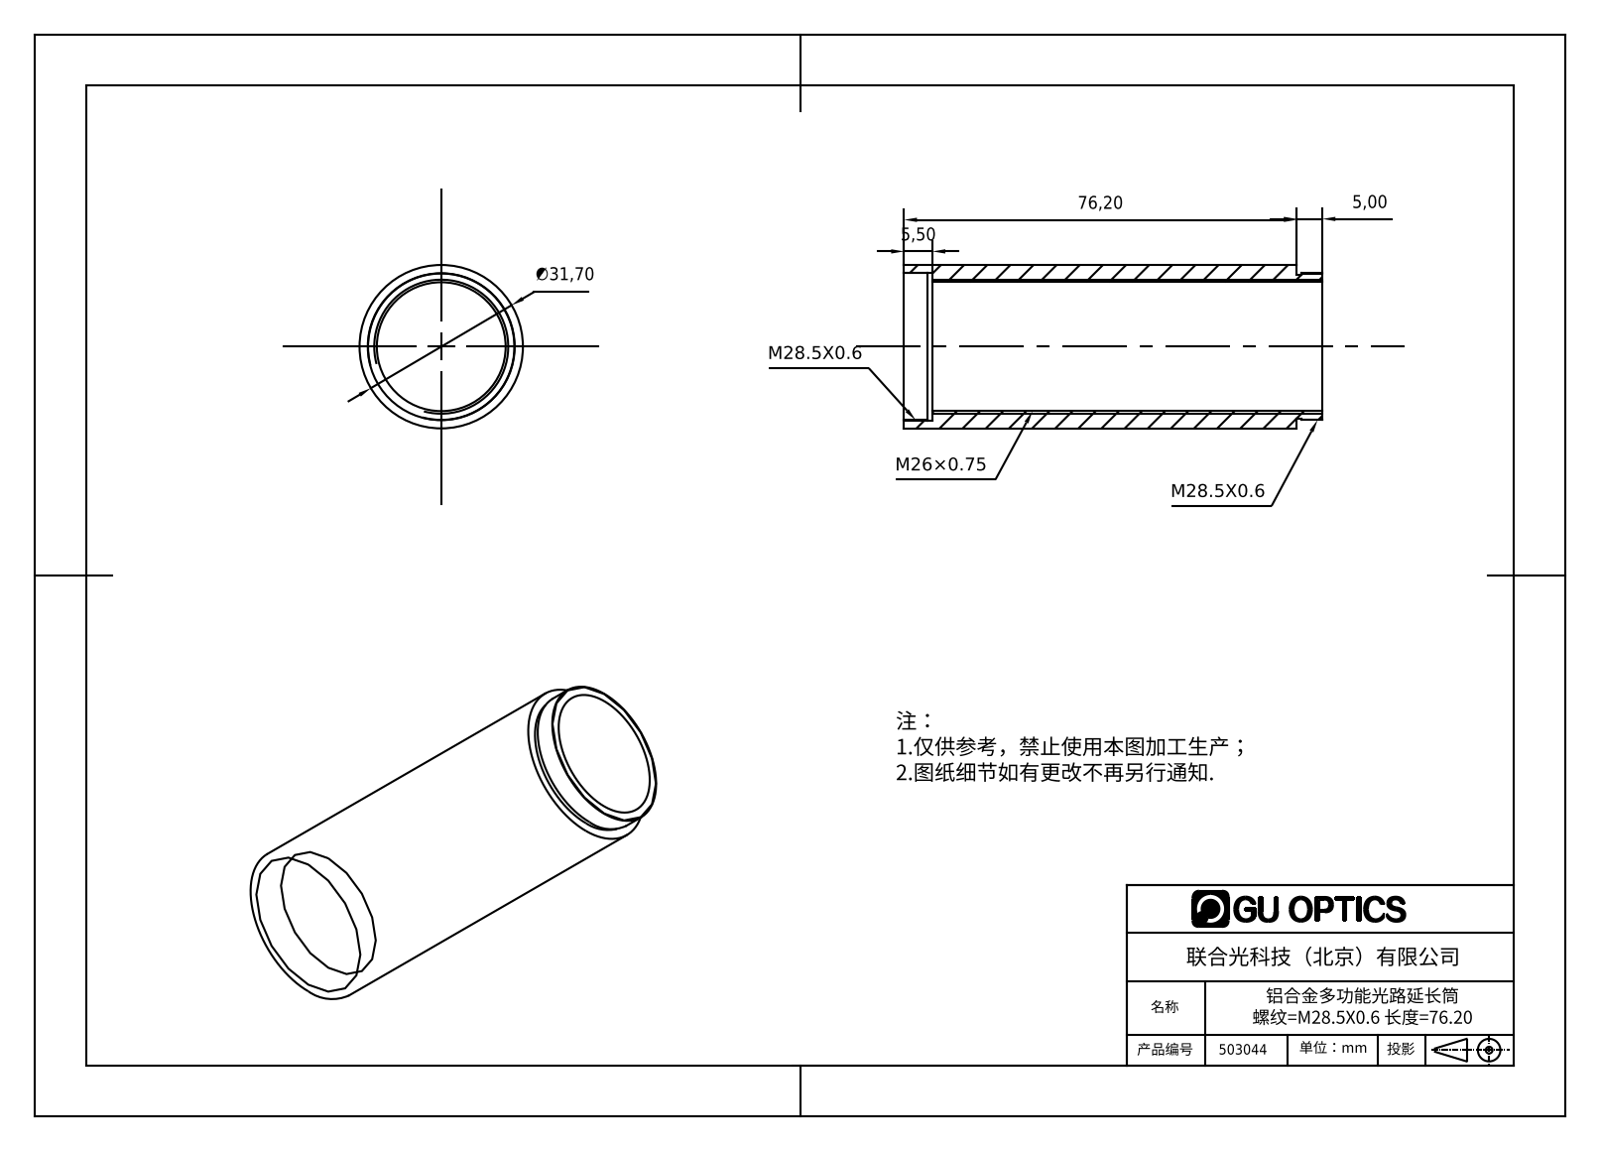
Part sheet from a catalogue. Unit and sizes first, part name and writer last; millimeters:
Units: millimetres
Overall size (bounding box): 81.2 × 31.7 × 31.7
Round holes (diameter × count): ⌀25 ×1, ⌀28.5 ×1, ⌀28.7 ×1
Round bosses / shafts (diameter × count): ⌀31.7 ×1, ⌀28 ×1
Main face-to-face distances: 70.7, 5.5, 76.2, 81.2, 75.7, 5, 1, 71.7, 77.2, 4
Volume: 22 631 mm³ · Surface area: 15 132 mm²
Bodies: 1 solid, 18 faces (6 planar, 12 cylindrical, 0 other)
Part name (STEP PRODUCT): 503044
STEP written by: SolidWorks 2016 (AUTOMOTIVE_DESIGN)
